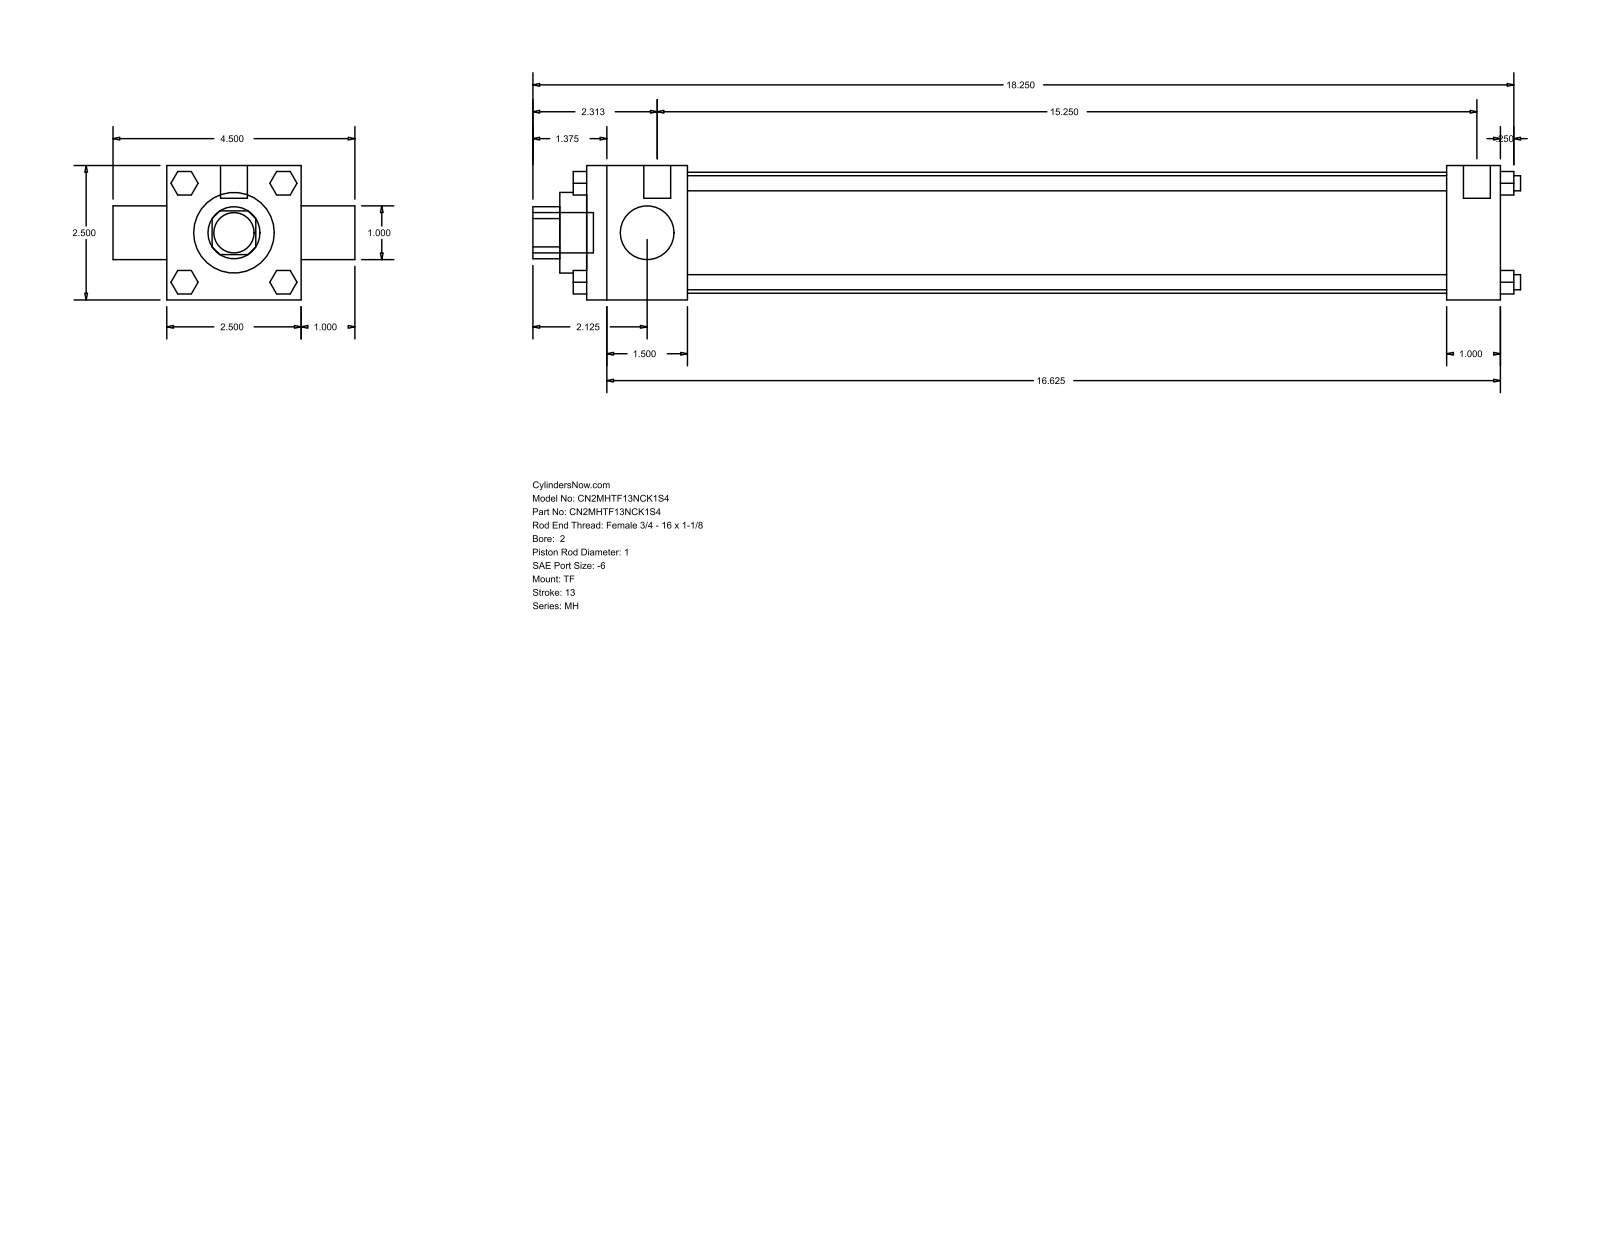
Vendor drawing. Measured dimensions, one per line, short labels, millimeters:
name: MH_TF__0200_1
written by: GSSL Pune (CONFIG_CONTROL_DESIGN)
unit: mm
bodies: 0 solids, 120 faces (92 planar, 28 cylindrical, 0 other)
size: 466.73 × 114.3 × 63.5
holes: 2× ⌀25.4, 1× ⌀38.1, 1× ⌀57.15
bosses: 4× ⌀7.14, 3× ⌀5.56, 2× ⌀12.7, 1× ⌀19.05
rounds: 1× R12.29
face distances: 63.5, 431.8, 25.4, 47.63, 406.4, 358.77, 384.17, 88.9, 444.5, 6.35
